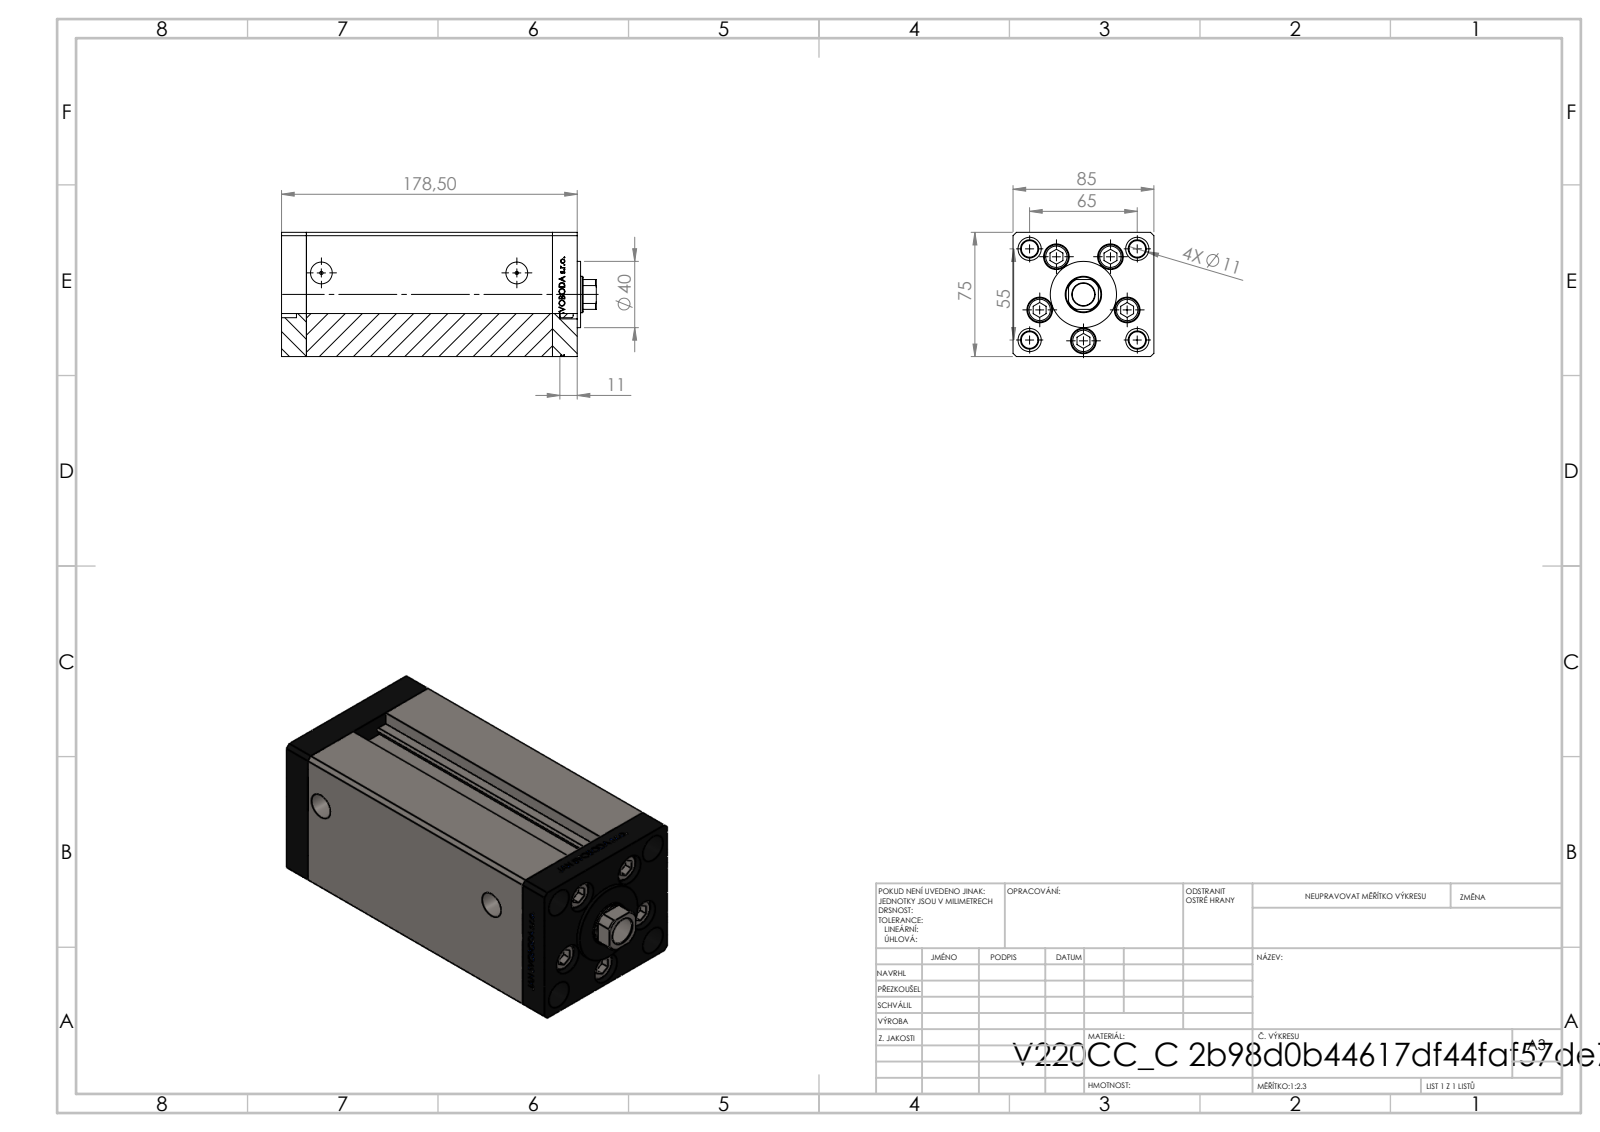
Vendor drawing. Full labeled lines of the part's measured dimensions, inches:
Part name (STEP PRODUCT): ALLEN BOLT; V220C FRONT; V220C_C MIDDLE; V220C_VC_C (+1 more)
STEP written by: SolidWorks 2019 (CONFIG_CONTROL_DESIGN)
Units: inches
Bodies: 13 solids, 1171 faces (542 planar, 167 cylindrical, 462 other)
Overall size (bounding box): 7.48 × 3.346 × 2.953
Volume: 57.69 in³ · Surface area: 279.8 in²
Round holes (diameter × count): ⌀0.433 ×9, ⌀0.61 ×5, ⌀0.394 ×4, ⌀0.551 ×4, ⌀0.079 ×2, ⌀0.518 ×2, ⌀0.531 ×1, ⌀0.571 ×1, ⌀0.866 ×1
Round bosses / shafts (diameter × count): ⌀0.315 ×5, ⌀0.571 ×4, ⌀1.575 ×1
Partial cylindrical surfaces — rounded edges, fillets, slot ends (radius × count): R0.037 ×2, R0.413 ×1
Main face-to-face distances: 3.346, 2.953, 0.591, 5.846, 6.437, 0.413, 7.028, 1.348, 5.679, 5.089
Hole centre spacings: 1.102, 1.676, 0.664, 0.755, 1.273, 1.28, 1.324, 1.47
